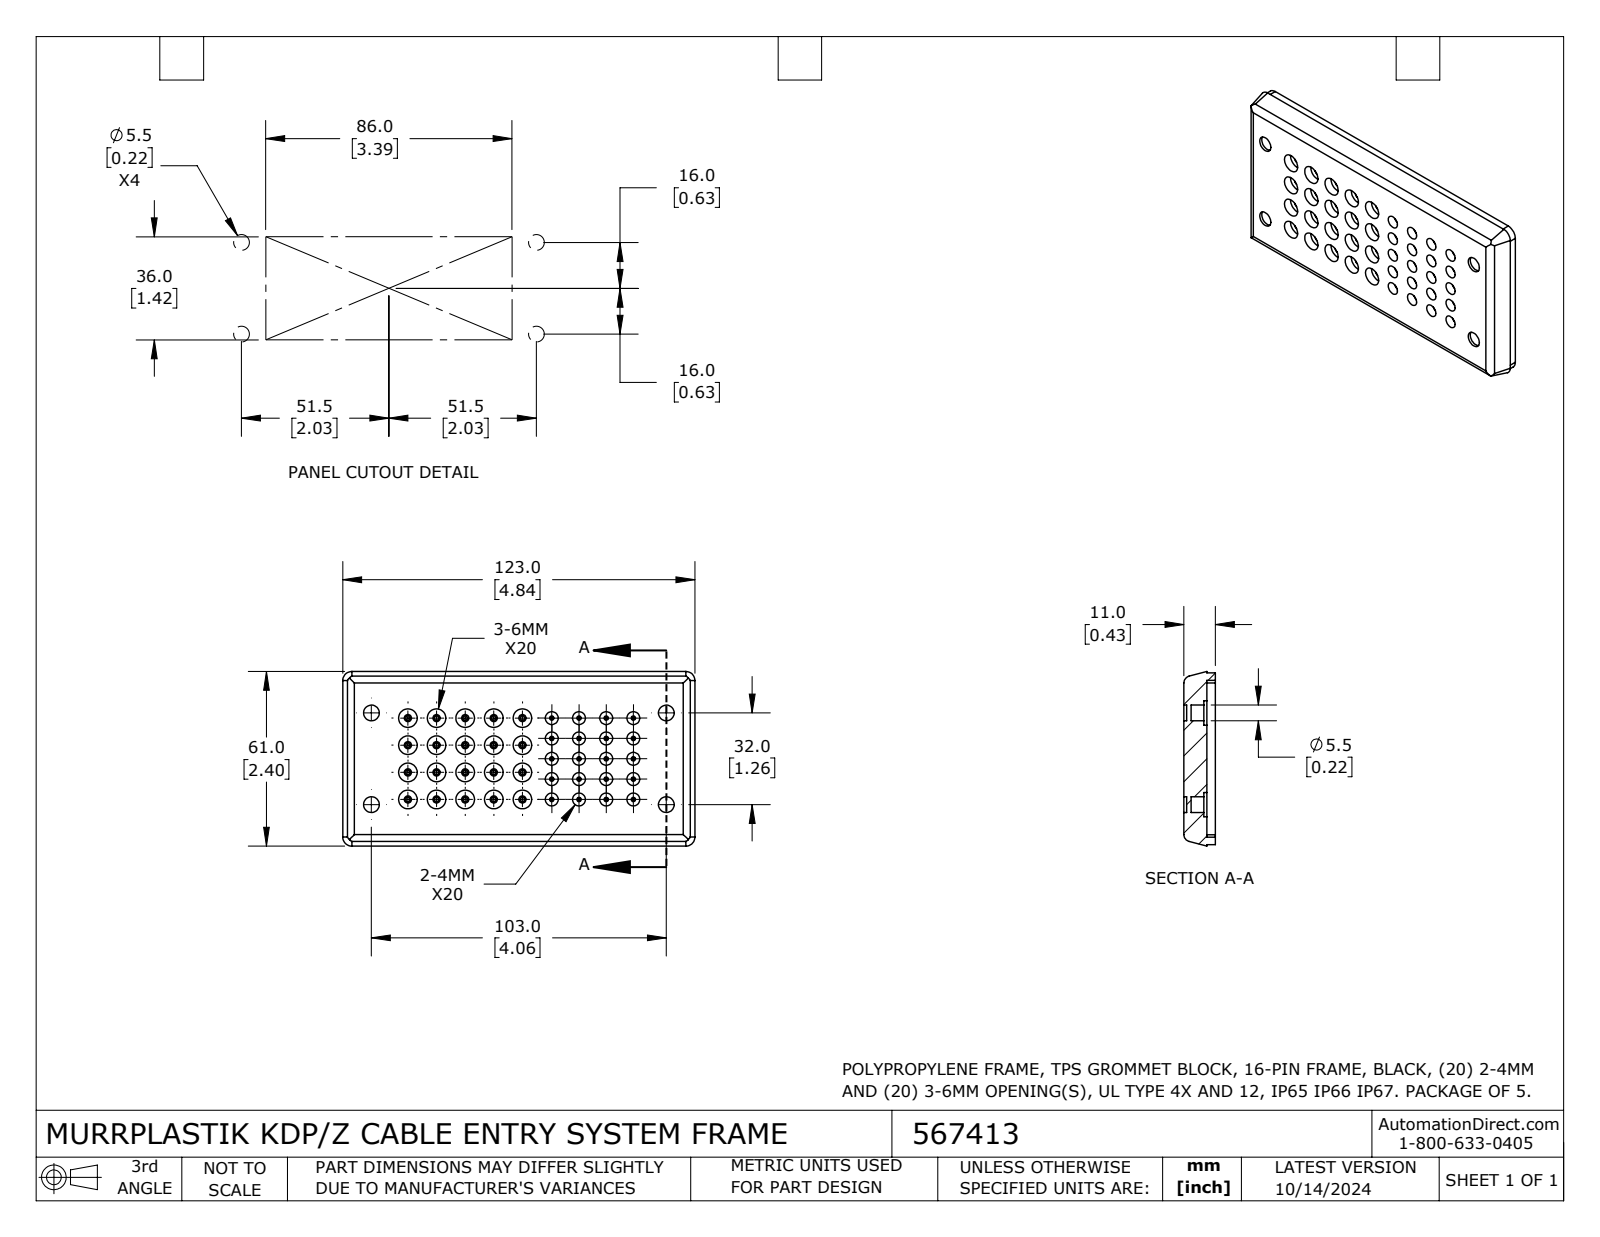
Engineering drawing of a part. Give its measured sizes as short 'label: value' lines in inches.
name: 567413
written by: SolidWorks 2023 (CONFIG_CONTROL_DESIGN)
unit: in
bodies: 1 solid, 460 faces (162 planar, 294 cylindrical, 4 other)
size: 4.843 × 2.402 × 0.433
volume: 2.748 in³; area: 37.99 in²
holes: 20× ⌀0.059, 20× ⌀0.098, 20× ⌀0.177, 20× ⌀0.256, 4× ⌀0.217, 4× ⌀0.335
bosses: 20× ⌀0.059, 20× ⌀0.039
rounds: 8× R0.012, 4× R0.035, 4× R0.098, 4× R0.138, 4× R0.244, 4× R0.266
face distances: 0.217, 0.098, 0.315, 0.118, 0.433, 0.197, 0.102, 0.386, 1.976, 2.26
hole spacings: 0.394, 0.542, 0.844, 0.787, 0.871, 1.085, 0.372, 0.746
